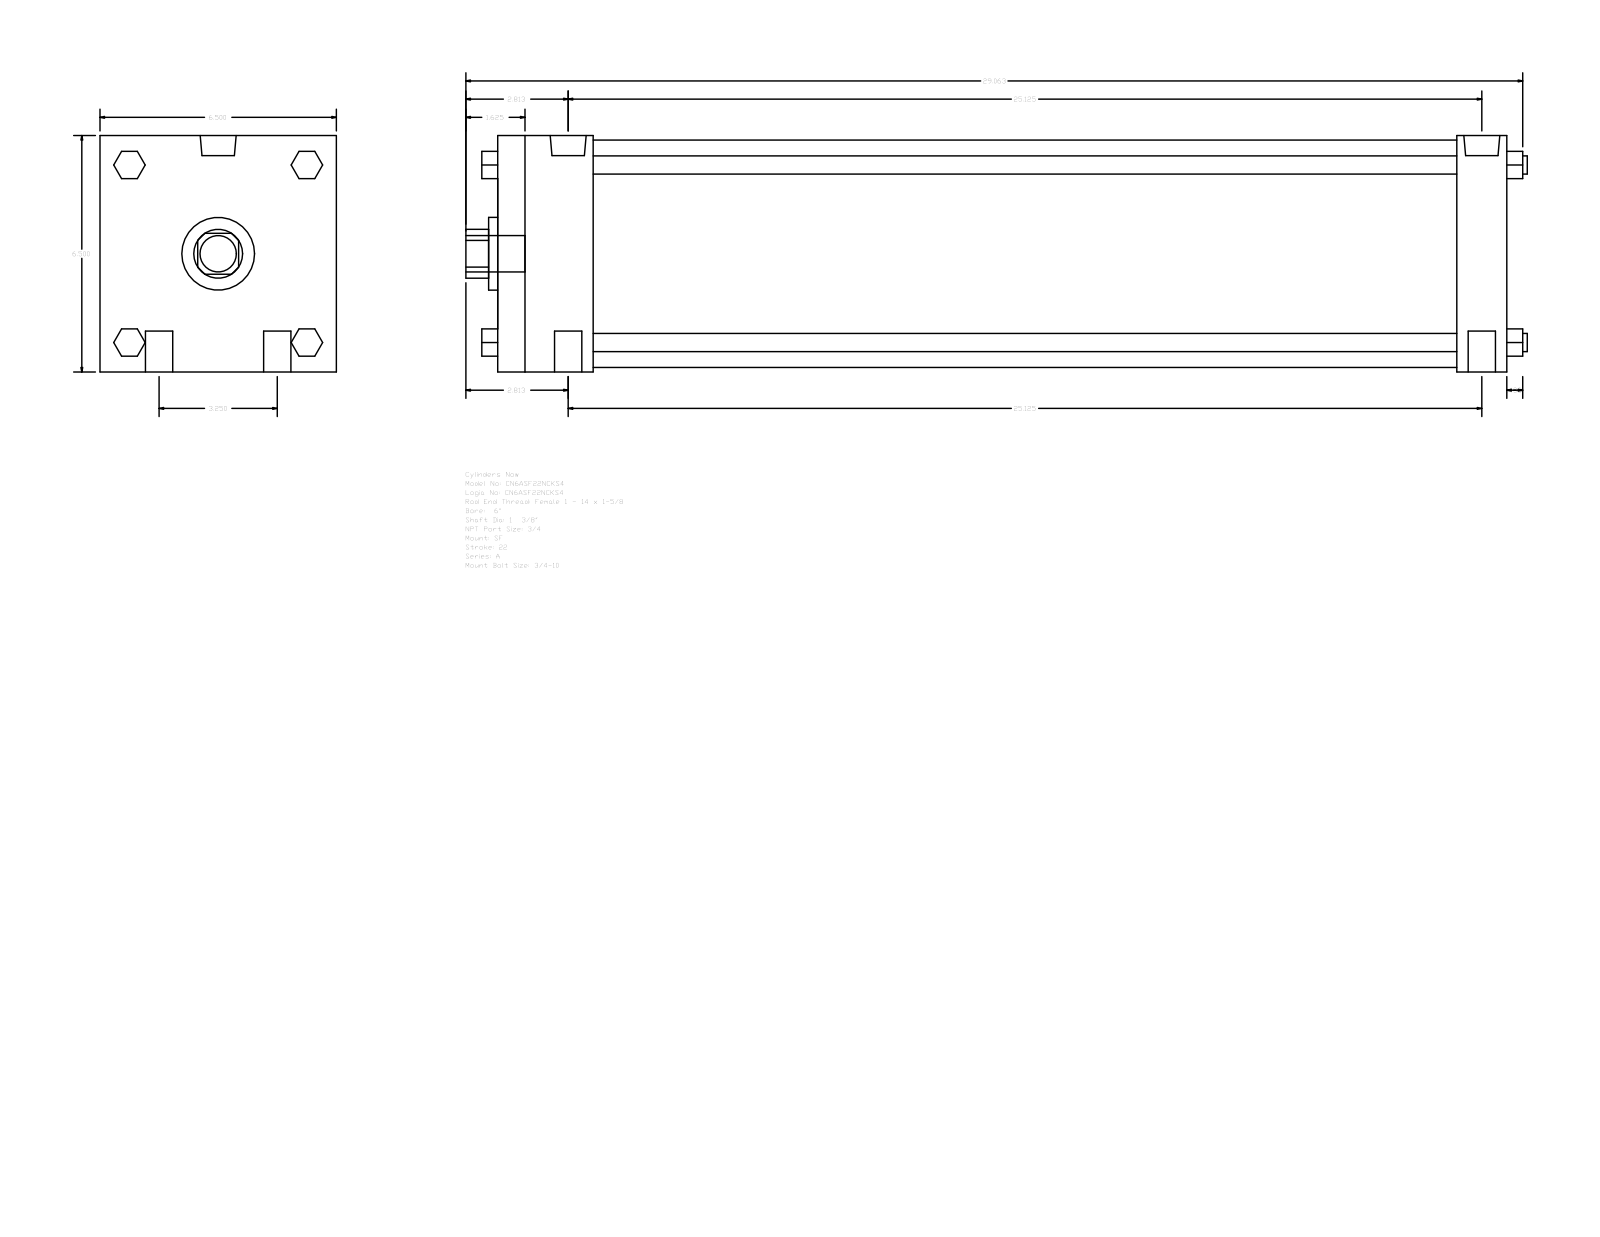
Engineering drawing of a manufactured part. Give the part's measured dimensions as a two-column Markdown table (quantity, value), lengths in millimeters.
| quantity | value |
| --- | --- |
| part name | A_SF__0600_1.375 |
| STEP written by | GSSL Pune (CONFIG_CONTROL_DESIGN) |
| units | millimeters |
| bodies | 0 solids, 124 faces (94 planar, 30 cylindrical, 0 other) |
| overall size | 741.36 × 165.1 × 165.1 |
| round holes (diameter × count) | 34.92 × 1, 50.8 × 1, 158.75 × 1 |
| round bosses / shafts (diameter × count) | 19.05 × 4, 12.7 × 4, 25.12 × 2, 15.08 × 2, 25.4 × 1 |
| partial cylindrical surfaces (radius × count) | 17.06 × 1 |
| main face-to-face distances | 165.1, 704.85, 669.92, 34.93, 66.67, 603.25, 638.18, 19.05, 61.97, 107.34 |
